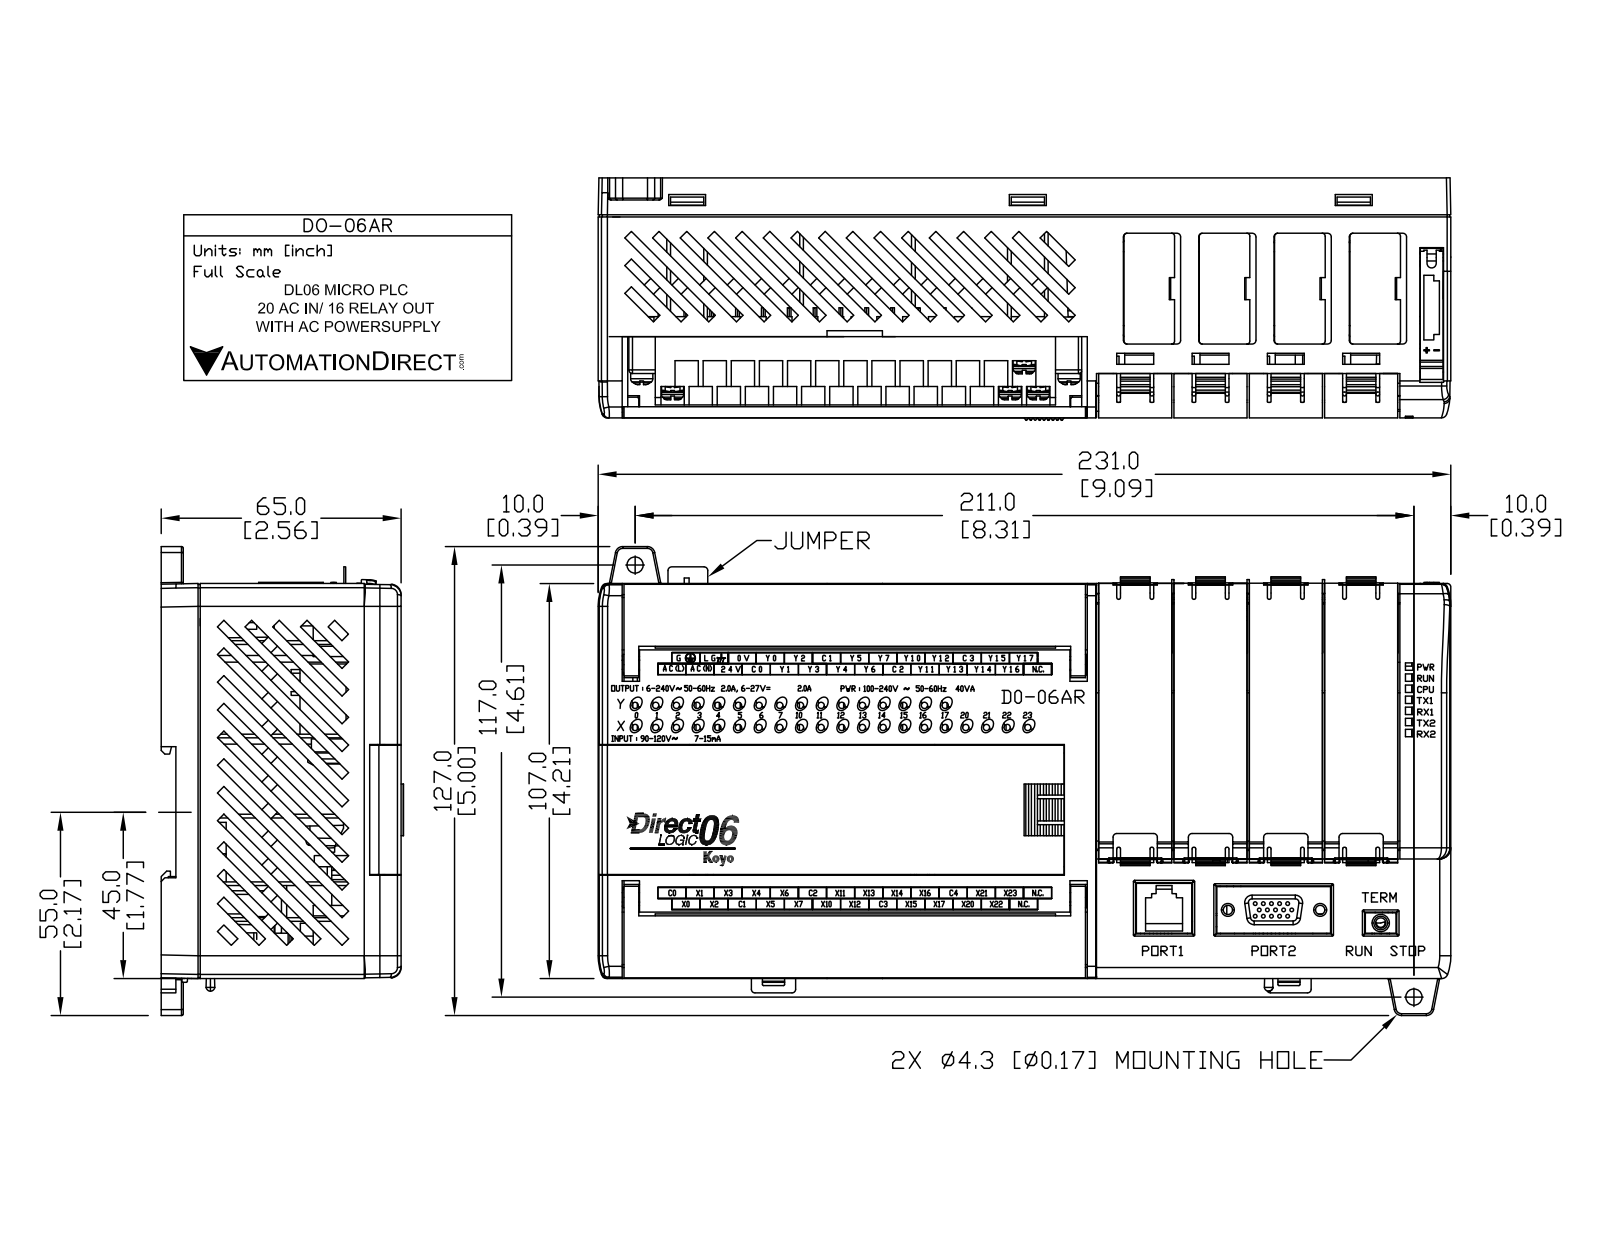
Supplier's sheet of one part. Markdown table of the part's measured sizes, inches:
| quantity | value |
| --- | --- |
| part name | D0-06AR |
| STEP written by | SolidWorks 2009 (AUTOMOTIVE_DESIGN) |
| units | inches |
| bodies | 1 solid, 1421 faces (930 planar, 189 cylindrical, 302 other) |
| overall size | 9.09 × 5.004 × 2.565 |
| volume | 16 in³ |
| surface area | 309 in² |
| round holes (diameter × count) | 0.118 × 4, 0.079 × 2, 0.17 × 2 |
| round bosses / shafts (diameter × count) | 0.185 × 54, 0.25 × 4, 0.175 × 1, 0.14 × 1 |
| partial cylindrical surfaces (radius × count) | 0.05 × 8, 0.065 × 5, 0.062 × 4, 0.08 × 4, 0.038 × 2, 0.063 × 2, 0.076 × 1, 2.471 × 1 |
| main face-to-face distances | 0.088, 0.088, 2.472, 0.157, 2.315, 2.56, 9.002, 2.384, 0.245, 2.227 |
| hole center spacings | 3.26, 4.612, 5.648, 0.676, 0.938, 1.399, 1.681, 2.203 |
